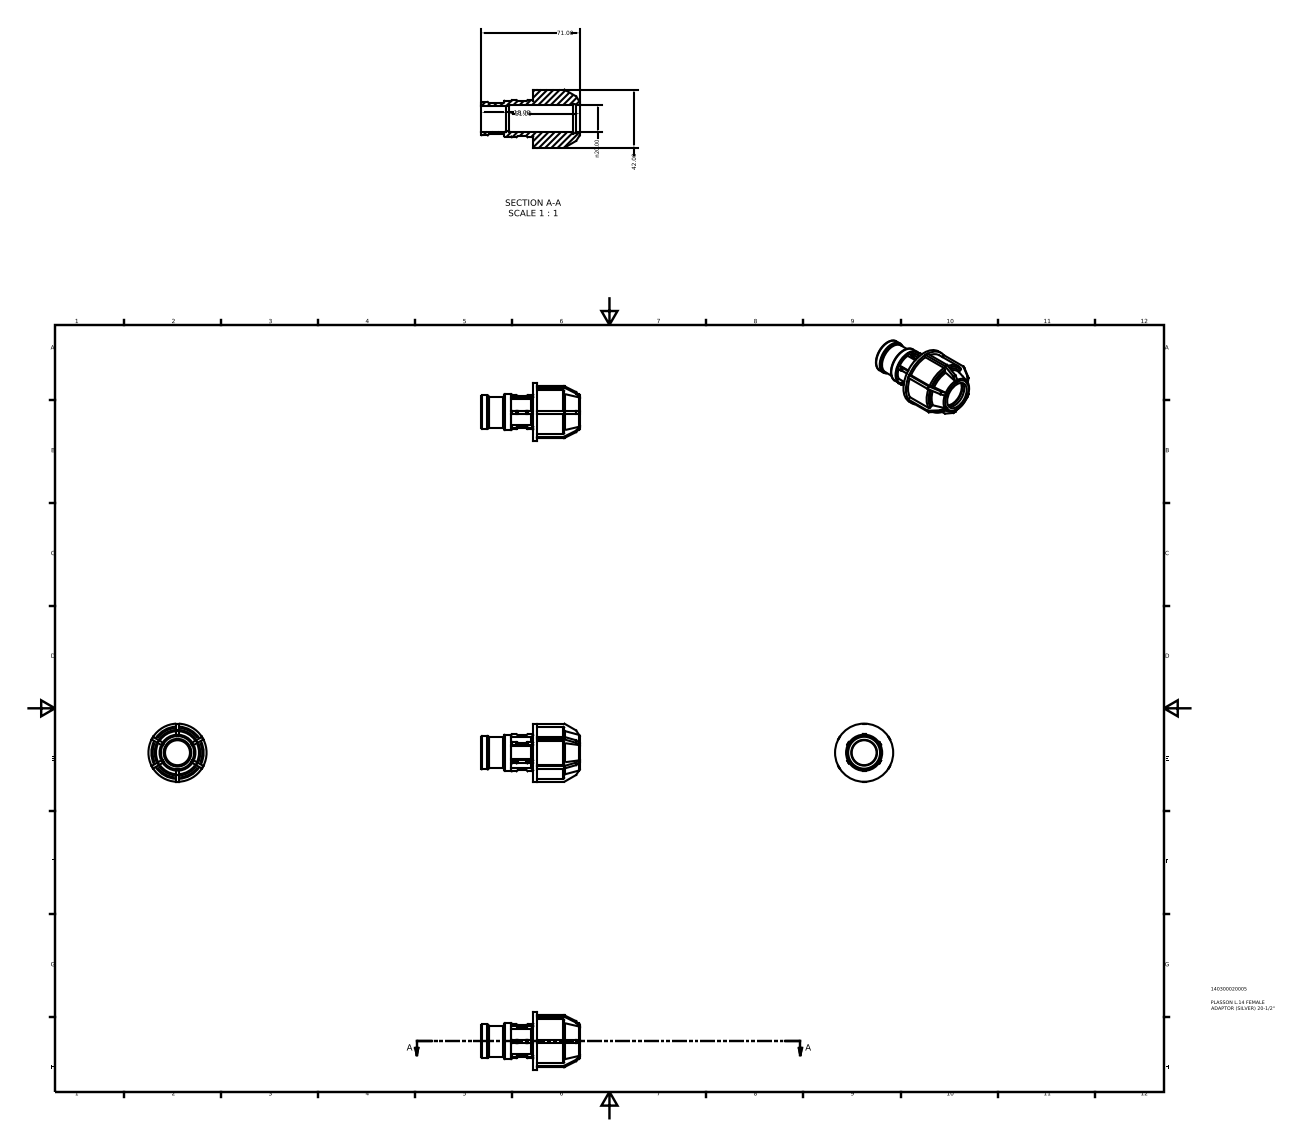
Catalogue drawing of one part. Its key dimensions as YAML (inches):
part_name: "140300020005"
step_written_by: "Autodesk Inventor 2015 (AUTOMOTIVE_DESIGN)"
units: inches
bodies: {solids: 1, faces: 262, planar: 160, cylindrical: 68, other: 34}
overall_size: [2.795, 1.654, 1.654]
volume: 1.754
surface_area: 22.19
round_holes:
  - {diameter: 0.709, count: 1}
  - {diameter: 0.733, count: 1}
  - {diameter: 0.787, count: 1}
round_bosses_or_shafts:
  - {diameter: 1.654, count: 1}
  - {diameter: 1.488, count: 1}
  - {diameter: 1.027, count: 1}
  - {diameter: 0.954, count: 1}
  - {diameter: 0.88, count: 1}
partial_cylinders:
  - {radius: 0.024, count: 48}
face_to_face_distances: [0.083, 0.1, 1.57, 0.787, 1.225, 1.47, 2.795, 1.325, 2.358, 0.888]
